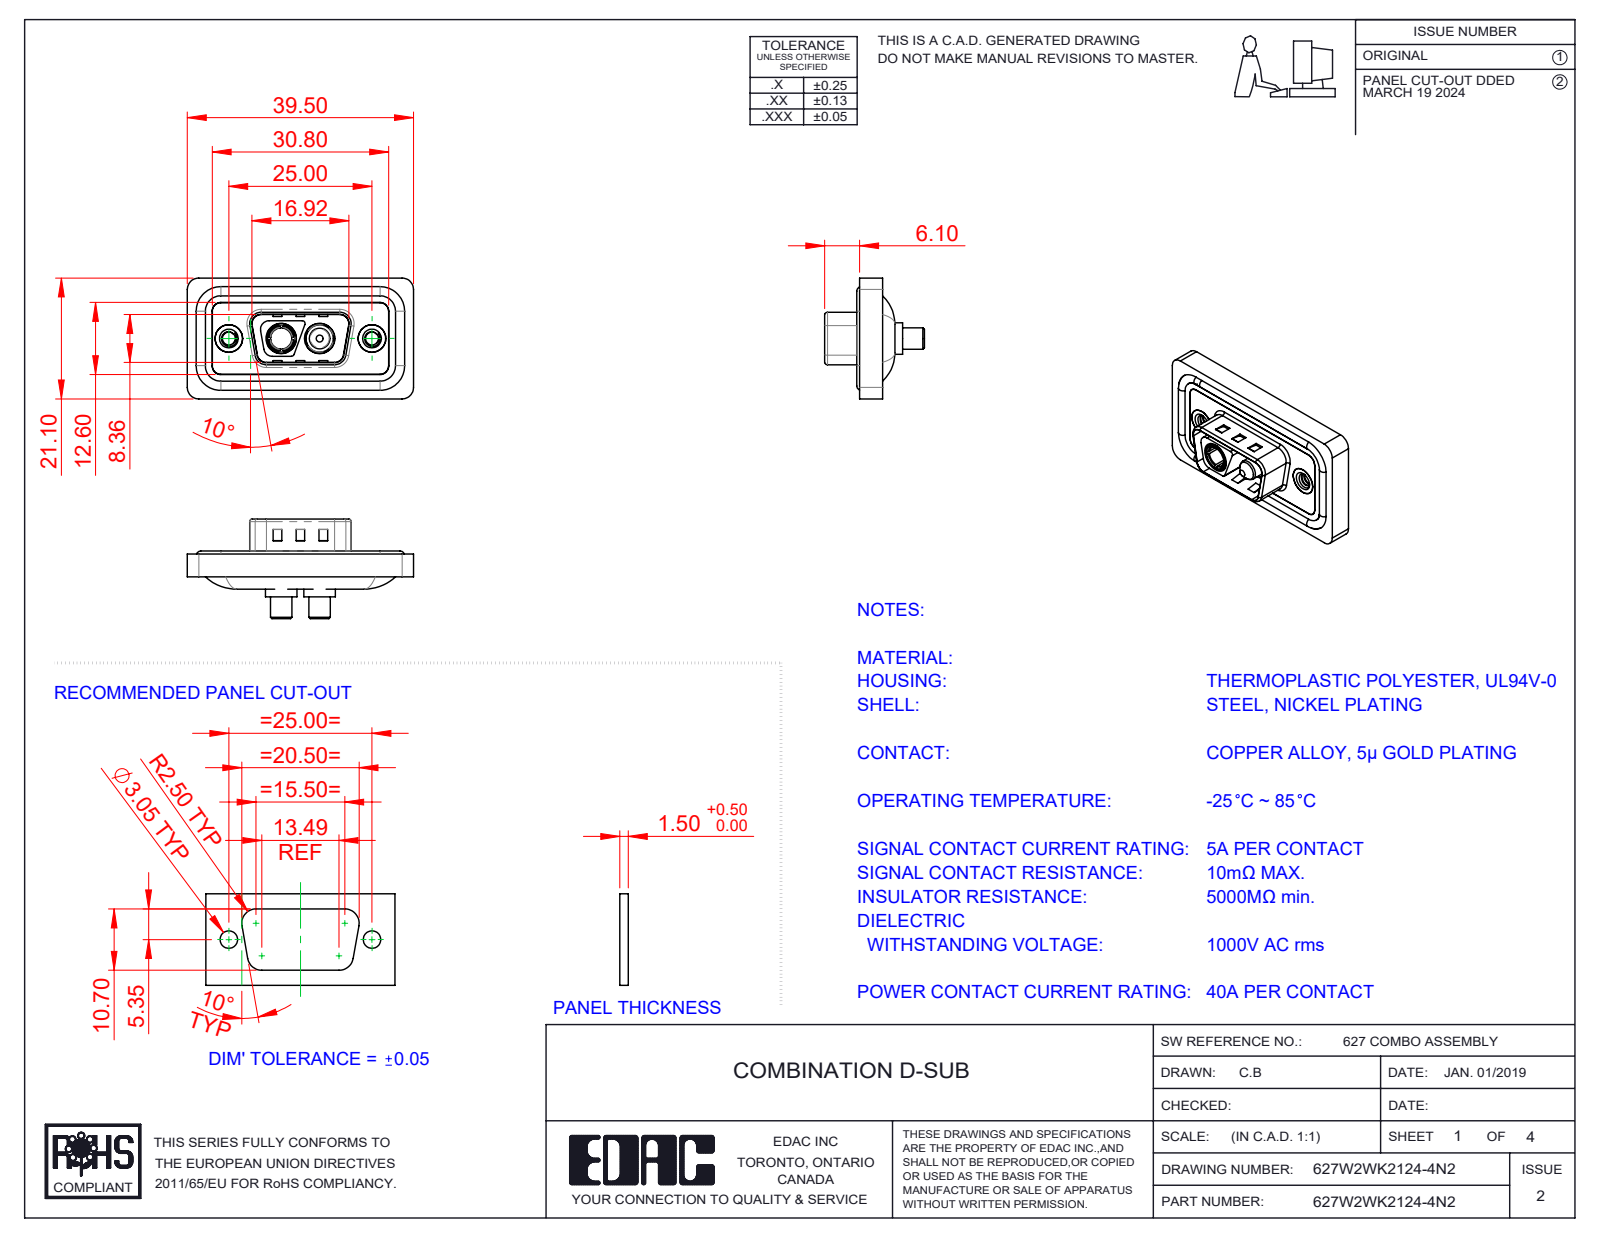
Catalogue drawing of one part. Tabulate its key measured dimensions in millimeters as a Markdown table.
| quantity | value |
| --- | --- |
| part name | Power Socket_40A S; 627Combo Threaded Rivet_2; Power Pin_40A S; 627Combo Housing_2WK2 (+4 more) |
| STEP written by | SolidWorks 2023 (CONFIG_CONTROL_DESIGN) |
| units | millimeters |
| bodies | 11 solids, 534 faces (189 planar, 227 cylindrical, 118 other) |
| overall size | 39.5 × 21.1 × 17.4 |
| volume | 4 591 mm³ |
| surface area | 7 364 mm² |
| round holes (diameter × count) | 2.26 × 2, 4 × 2, 4.8 × 2, 4.85 × 2, 5 × 2, 5.3 × 2, 3.7 × 1 |
| round bosses / shafts (diameter × count) | 1.6 × 4, 5.5 × 2, 5.2 × 2, 4.9 × 2, 4.75 × 2, 3.75 × 2, 4.96 × 1, 3.6 × 1 |
| partial cylindrical surfaces (radius × count) | 1.5 × 24, 2 × 18, 0.5 × 10, 1.6 × 8, 0.25 × 4, 0.6 × 4, 0.65 × 4, 0.9 × 4 |
| main face-to-face distances | 0.4, 1.1, 2.9, 0.5, 3.1, 1.6, 1.5, 2.5, 4, 1.8 |
| hole center spacings | 9.14, 15.86, 6.72, 25 |
